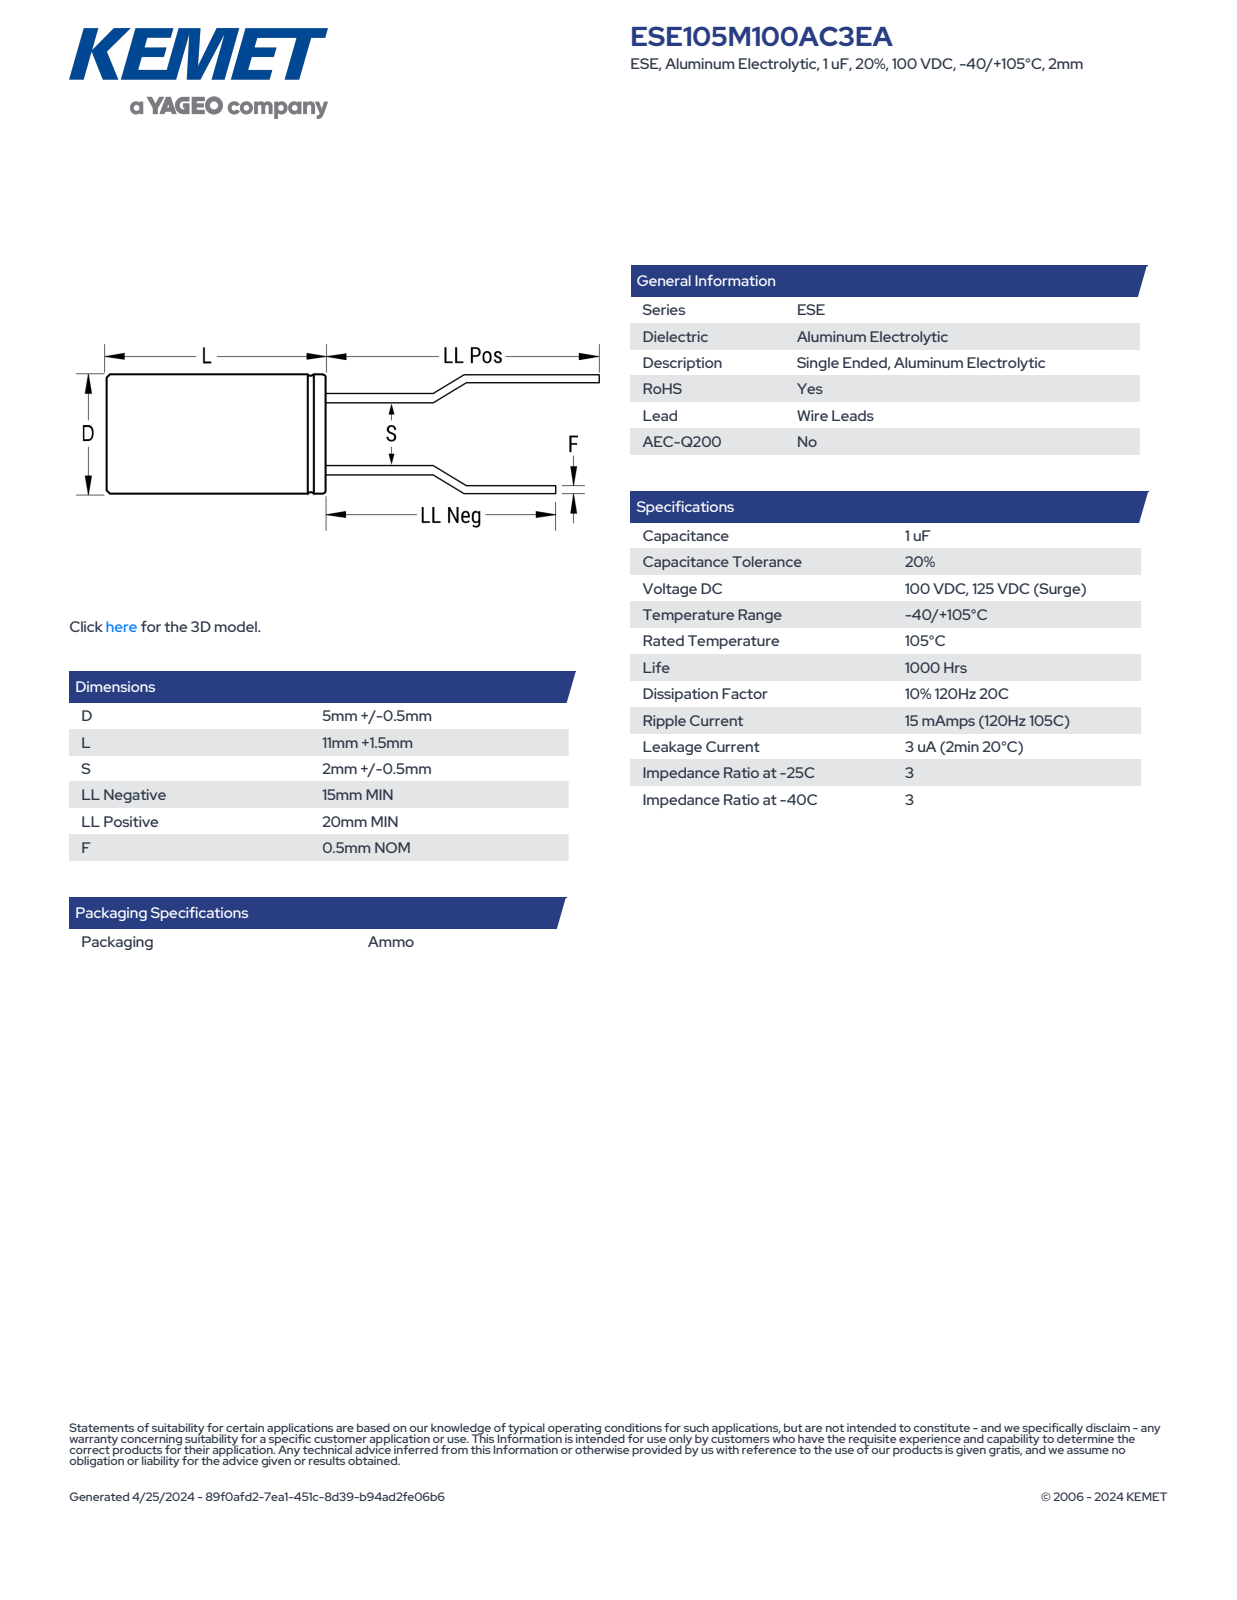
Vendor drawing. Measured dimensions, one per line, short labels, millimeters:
name: CAR_KTRS_5X11_D5.5L12.5S2F0.5
written by: SolidWorks 2014 (AUTOMOTIVE_DESIGN)
unit: mm
bodies: 4 solids, 73 faces (61 planar, 8 cylindrical, 4 other)
size: 32.51 × 5.5 × 5.5
volume: 302 mm³; area: 325 mm²
bosses: 2× ⌀0.5, 1× ⌀5.5
face distances: 12.5, 12.51, 27.51, 32.51, 27.5, 32.5, 15, 20, 5, 0.66
